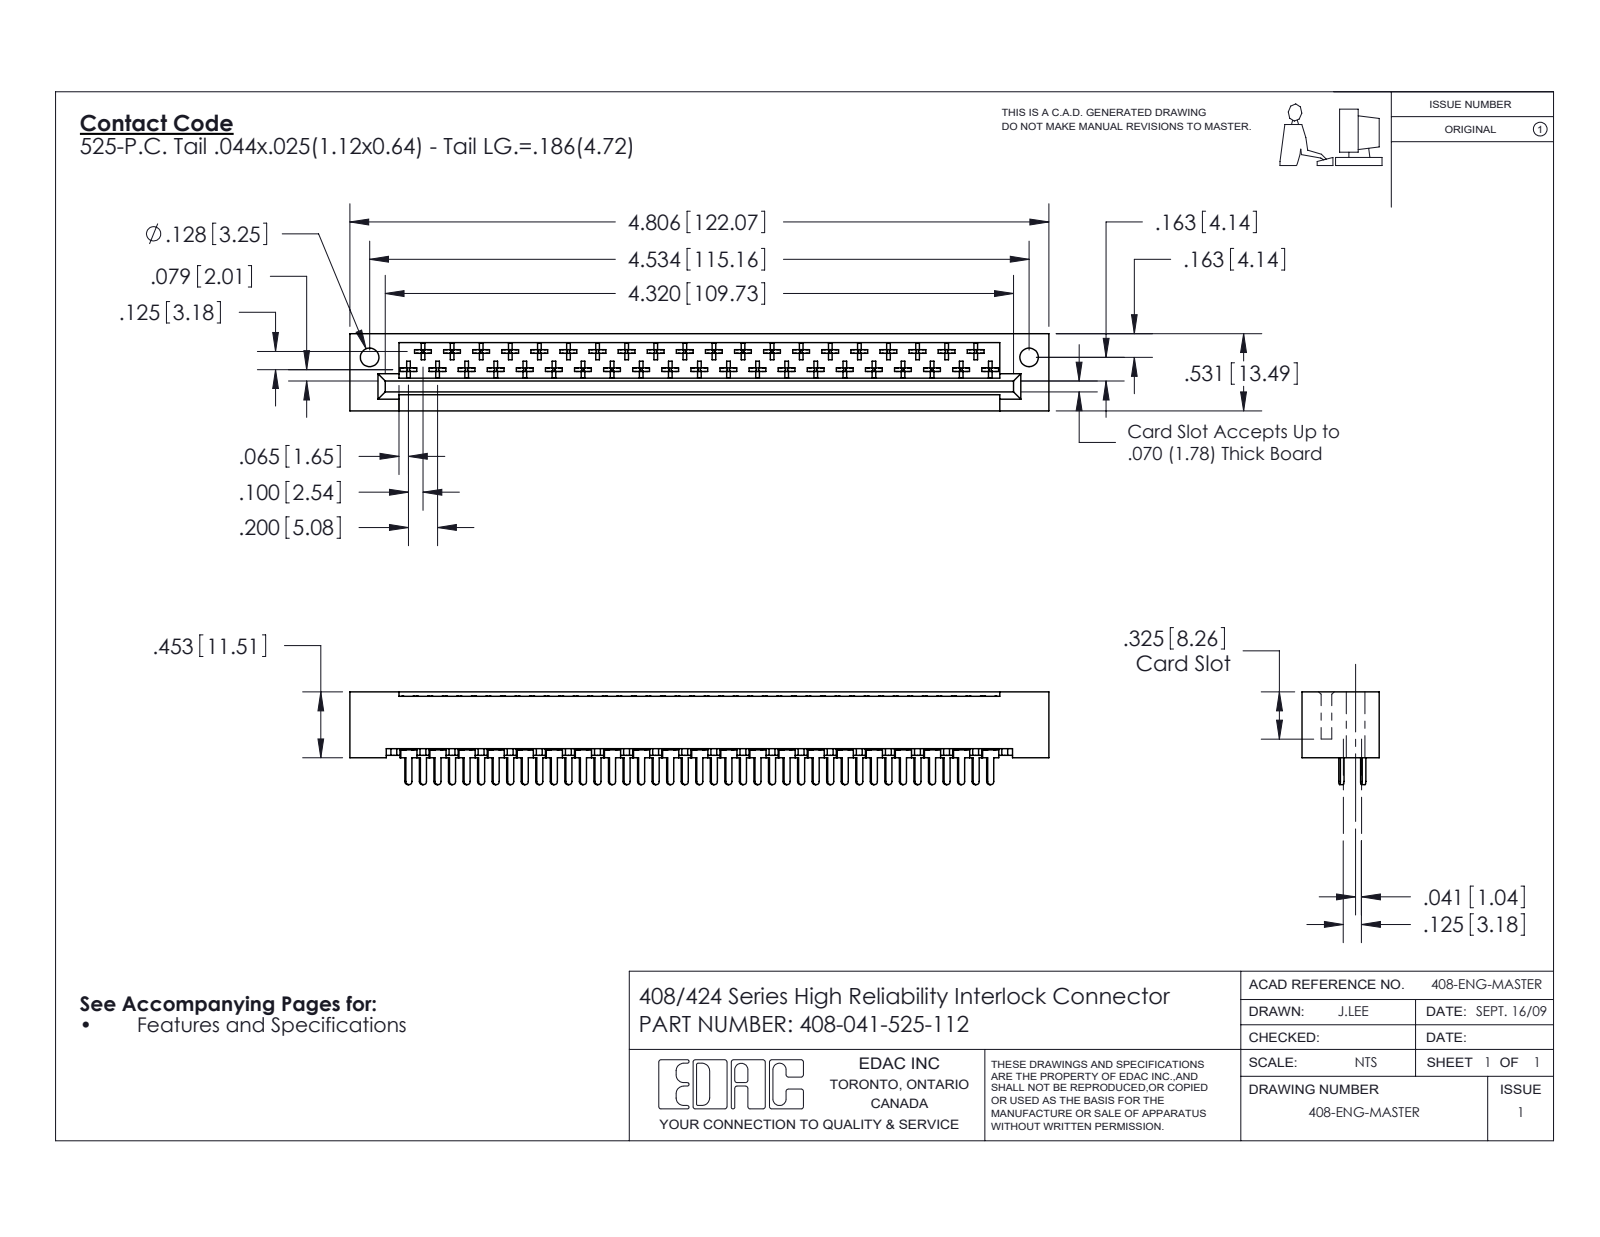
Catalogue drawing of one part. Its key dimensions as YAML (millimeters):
part_name: "408-047-525-112; 408-290-001_408-290-125 - Bottom; 408 Part_041 - 1; 408-290-001_408-290-125 - Top"
step_written_by: "SolidWorks 2016 (CONFIG_CONTROL_DESIGN)"
units: millimeters
bodies: {solids: 42, faces: 2299, planar: 1758, cylindrical: 377, other: 164}
overall_size: [122.1, 16.2, 13.5]
volume: 14000
surface_area: 16840
round_holes:
  - {diameter: 3.3, count: 2}
partial_cylinders:
  - {radius: 0.3, count: 246}
  - {radius: 0.5, count: 43}
  - {radius: 0.6, count: 41}
face_to_face_distances: [13.5, 3.2, 2.5, 0.6, 0.6, 10.2, 6.6, 6.9, 6, 7.5]
hole_center_spacings: [115.2]
